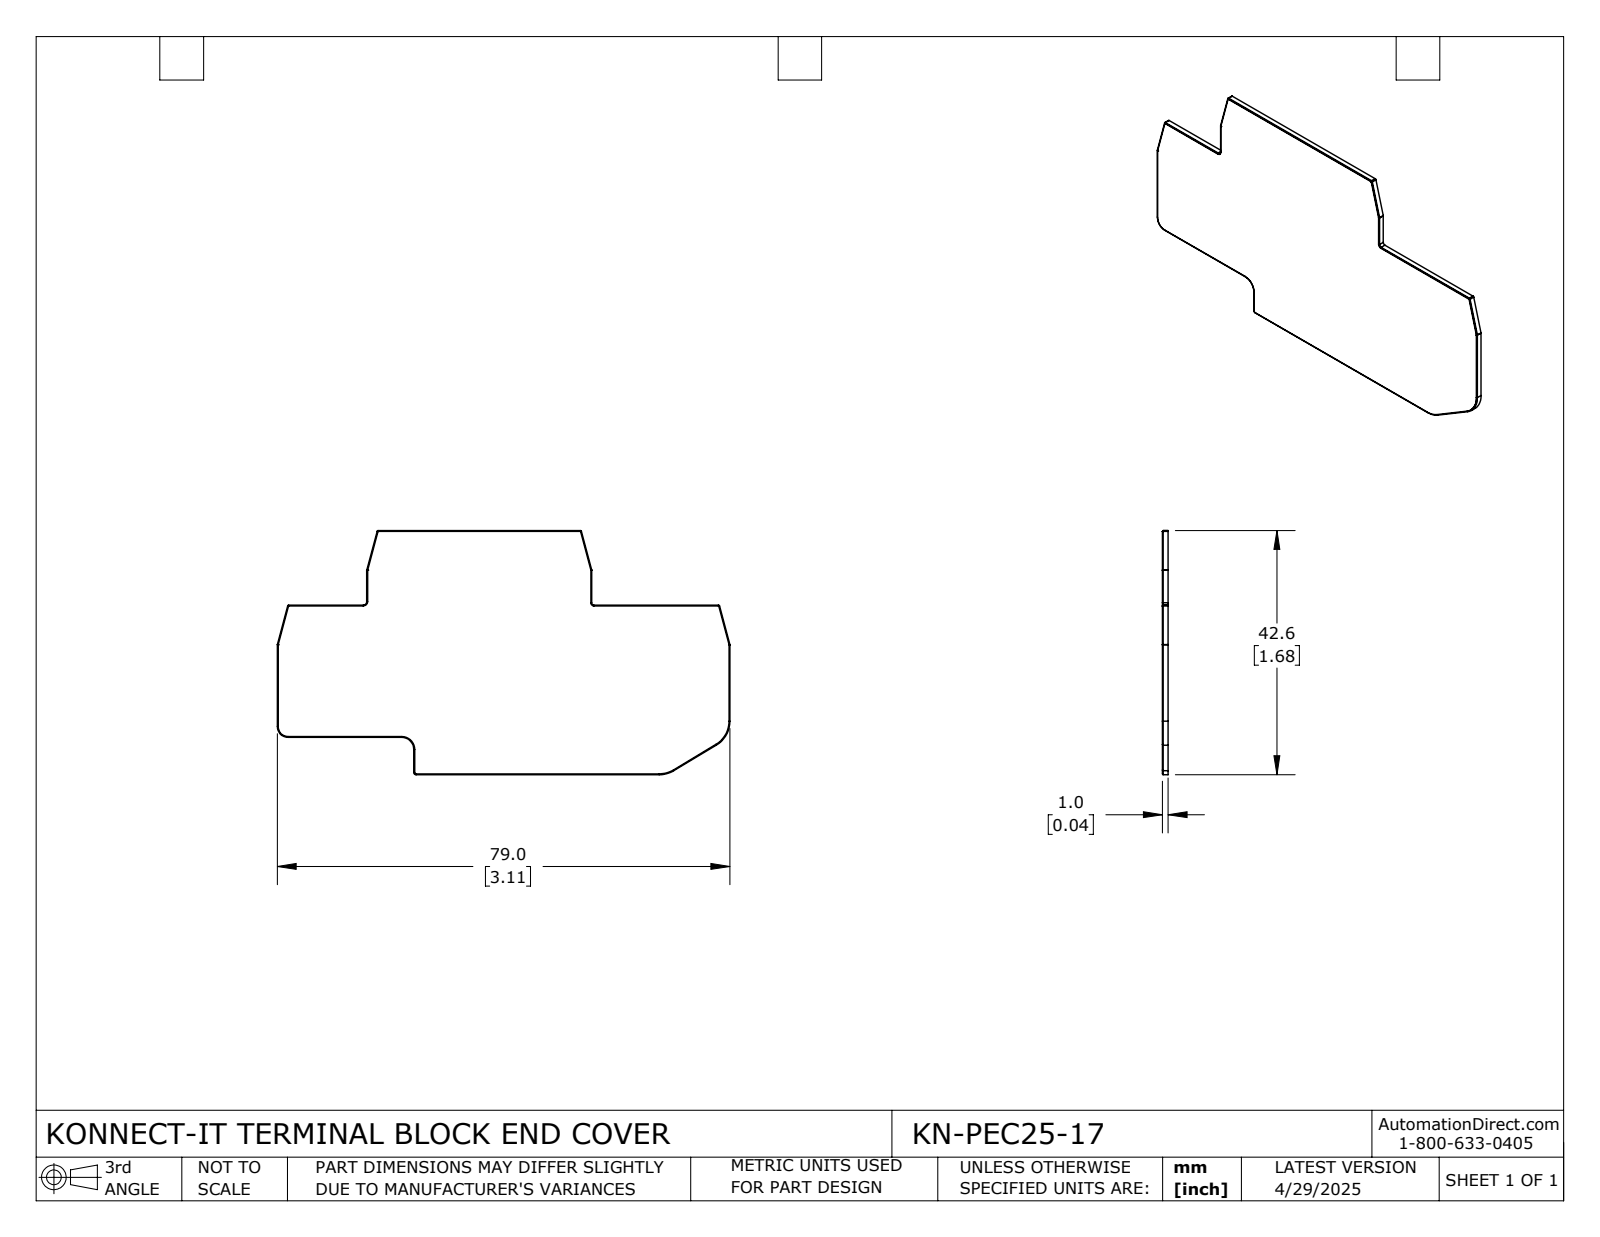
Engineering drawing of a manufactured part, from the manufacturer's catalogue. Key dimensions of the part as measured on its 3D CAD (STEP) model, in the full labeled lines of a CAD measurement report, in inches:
Part name (STEP PRODUCT): KN-PEC25-17
STEP written by: SolidWorks 2024 (CONFIG_CONTROL_DESIGN)
Units: inches
Bodies: 1 solid, 63 faces (33 planar, 30 cylindrical, 0 other)
Overall size (bounding box): 3.112 × 1.678 × 0.039
Volume: 0.16 in³ · Surface area: 8.519 in²
Partial cylindrical surfaces — rounded edges, fillets, slot ends (radius × count): R0.008 ×8, R0.016 ×2, R0.187 ×2, R0.193 ×2, R0.01 ×1, R0.022 ×1, R0.024 ×1, R0.03 ×1
Main face-to-face distances: 0.039, 0.512, 0.035, 1.678, 1.166, 0.256, 0.909, 1.422, 3.112, 1.672
